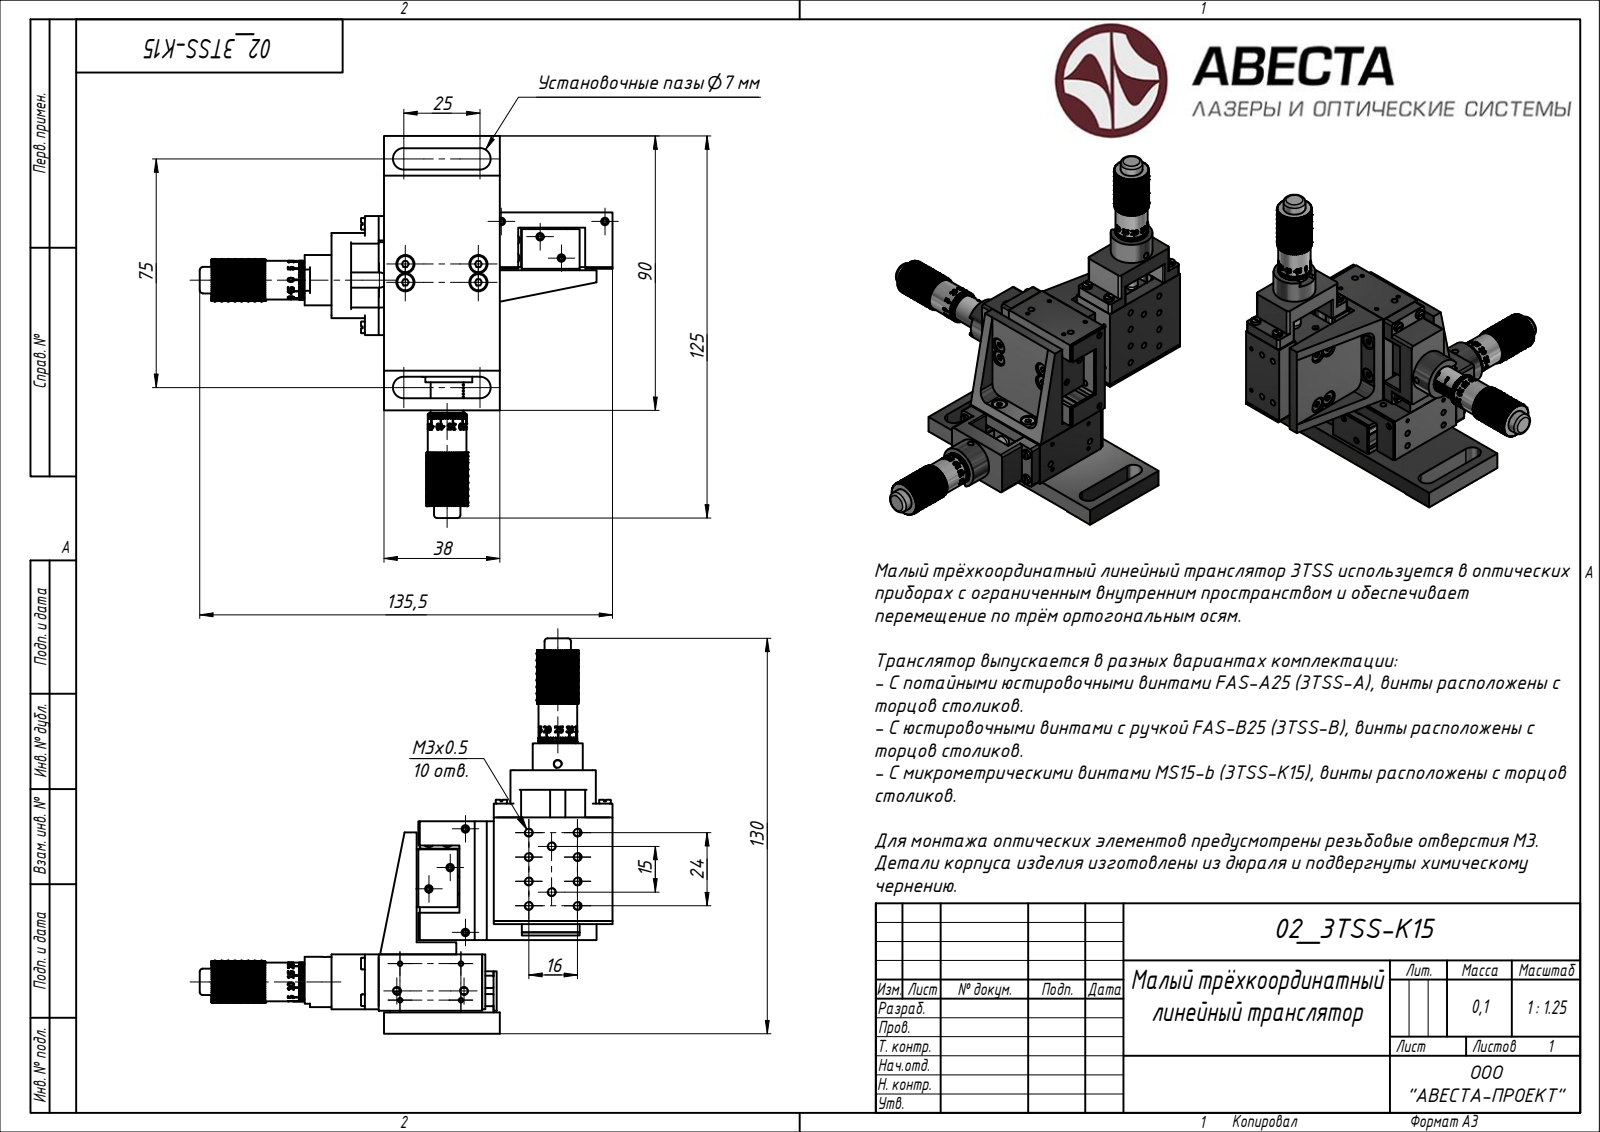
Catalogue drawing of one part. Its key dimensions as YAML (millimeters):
step_written_by: "Rhino 7.34 (AUTOMOTIVE_DESIGN)"
units: millimeters
bodies: {solids: 8, faces: 11048, planar: 8809, cylindrical: 1153, other: 1086}
overall_size: [135.54, 129.71, 125.29]
volume: 133076
surface_area: 81789
round_holes:
  - {diameter: 2.46, count: 41}
  - {diameter: 1.57, count: 19}
  - {diameter: 2.5, count: 18}
  - {diameter: 3.4, count: 16}
  - {diameter: 6, count: 15}
  - {diameter: 2.46, count: 13}
  - {diameter: 1.5, count: 12}
  - {diameter: 2.4, count: 12}
  - {diameter: 6.5, count: 8}
  - {diameter: 1.57, count: 7}
  - {diameter: 5.5, count: 3}
  - {diameter: 9.5, count: 3}
round_bosses_or_shafts:
  - {diameter: 4, count: 18}
  - {diameter: 5.54, count: 12}
  - {diameter: 3.8, count: 12}
  - {diameter: 3, count: 12}
  - {diameter: 2, count: 12}
  - {diameter: 5.35, count: 4}
  - {diameter: 16.5, count: 3}
  - {diameter: 13.5, count: 3}
partial_cylinders:
  - {radius: 0.5, count: 24}
  - {radius: 1, count: 24}
  - {radius: 2, count: 12}
  - {radius: 1.23, count: 9}
  - {radius: 1.23, count: 9}
  - {radius: 3.5, count: 4}
  - {radius: 4, count: 4}
  - {radius: 5.39, count: 3}
face_to_face_distances: [0.5, 13.5, 4.5, 2, 1.5, 12, 11.5, 9, 39, 23]
hole_center_spacings: [16, 6, 8, 17.89, 7, 20.88, 12, 22.63]
